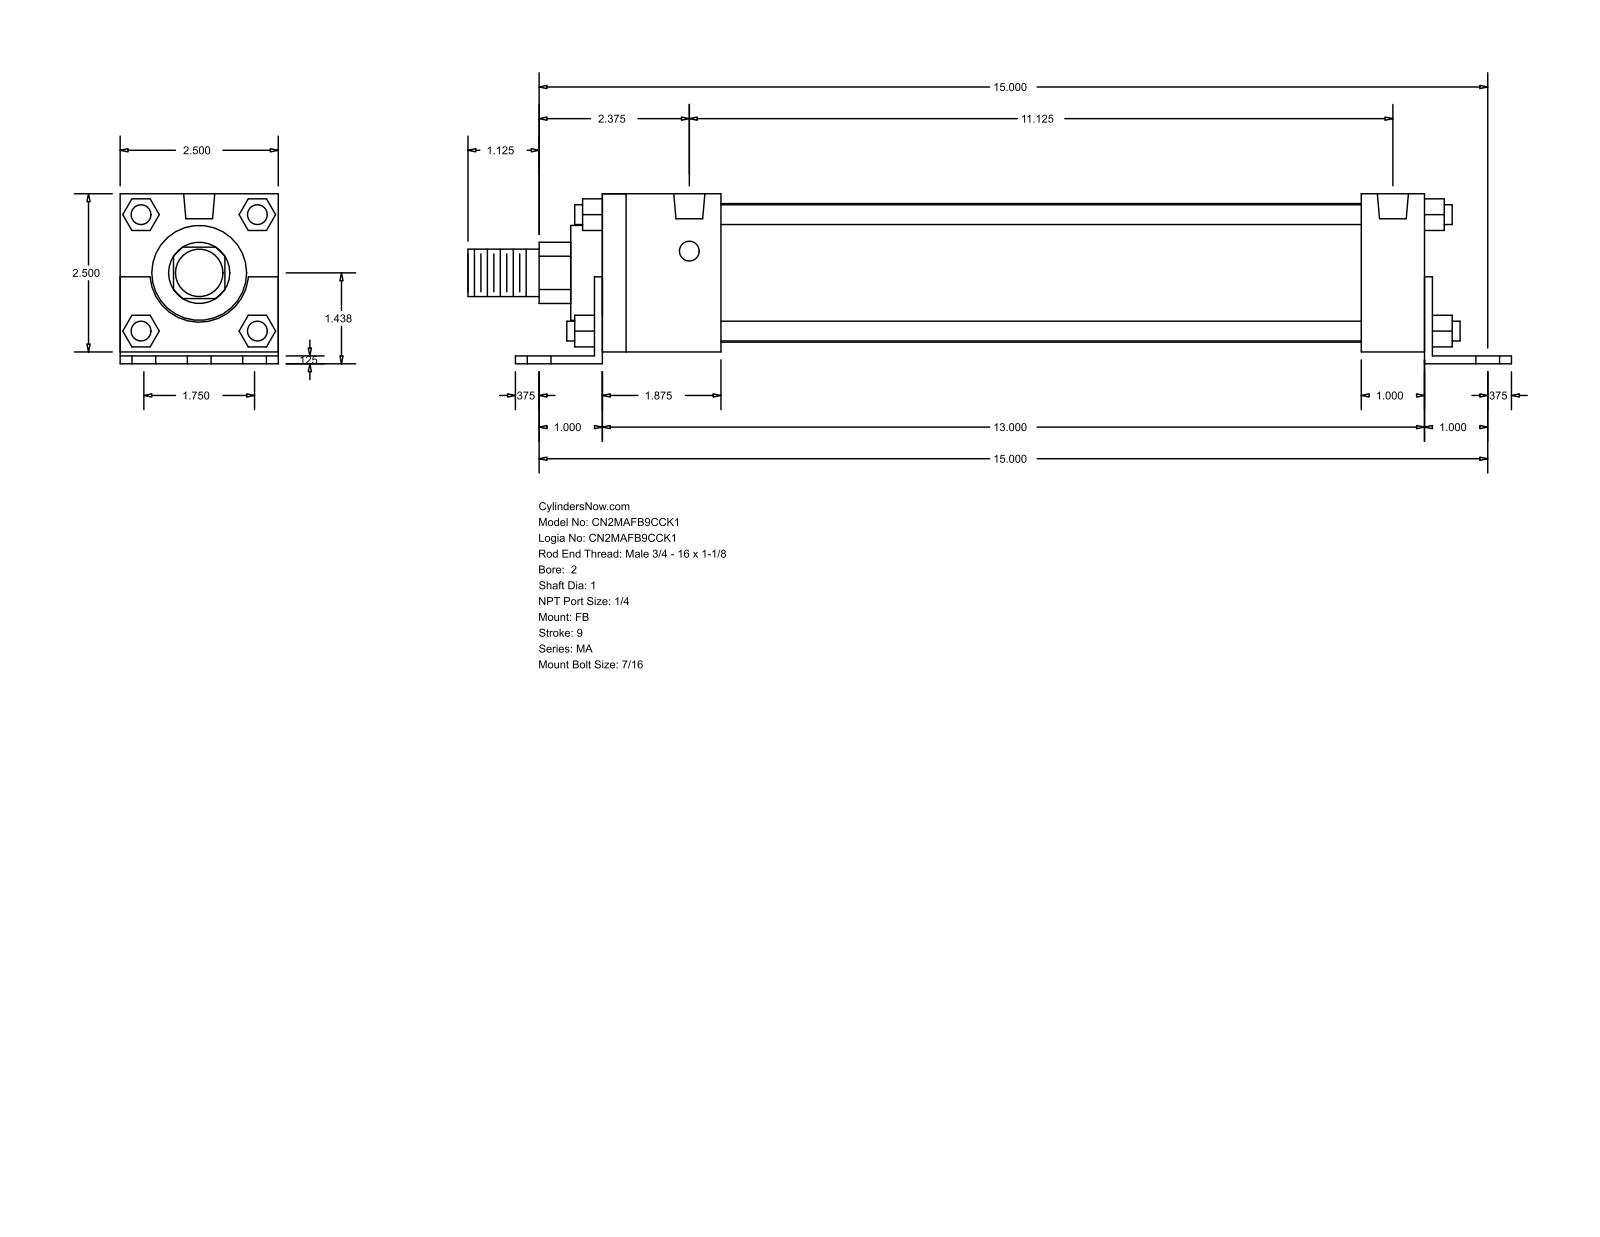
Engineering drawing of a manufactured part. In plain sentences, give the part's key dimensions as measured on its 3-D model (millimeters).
The part is named "MA_FB__0200_1". Its 3-D file was written by "GSSL Pune (CONFIG_CONTROL_DESIGN)". It is 0 solids with 140 faces: 105 planar, 35 cylindrical and 0 other. Overall it measures 419.1 by 68.26 by 63.5 millimeters. Round holes: 6 of diameter 11.11, 4 of diameter 7.94, 2 of diameter 12.49. Round bosses or shafts: 4 of diameter 7.94, 1 of diameter 55.63, 1 of diameter 38.1, 1 of diameter 25.4, 1 of diameter 19.05. Partial cylindrical surfaces (rounded edges, fillets, slot ends): 1 of radius 12.29, 1 of radius 19.81. The main face-to-face distances are 63.5, 3.17, 4.76, 68.26, 1.59, 65.09, 333.37, 12.7, 330.2, 28.57. The hole center spacings are 22.23, 381.65, 381, 44.11, 44.46, 64.3, 282.57, 321.44.
